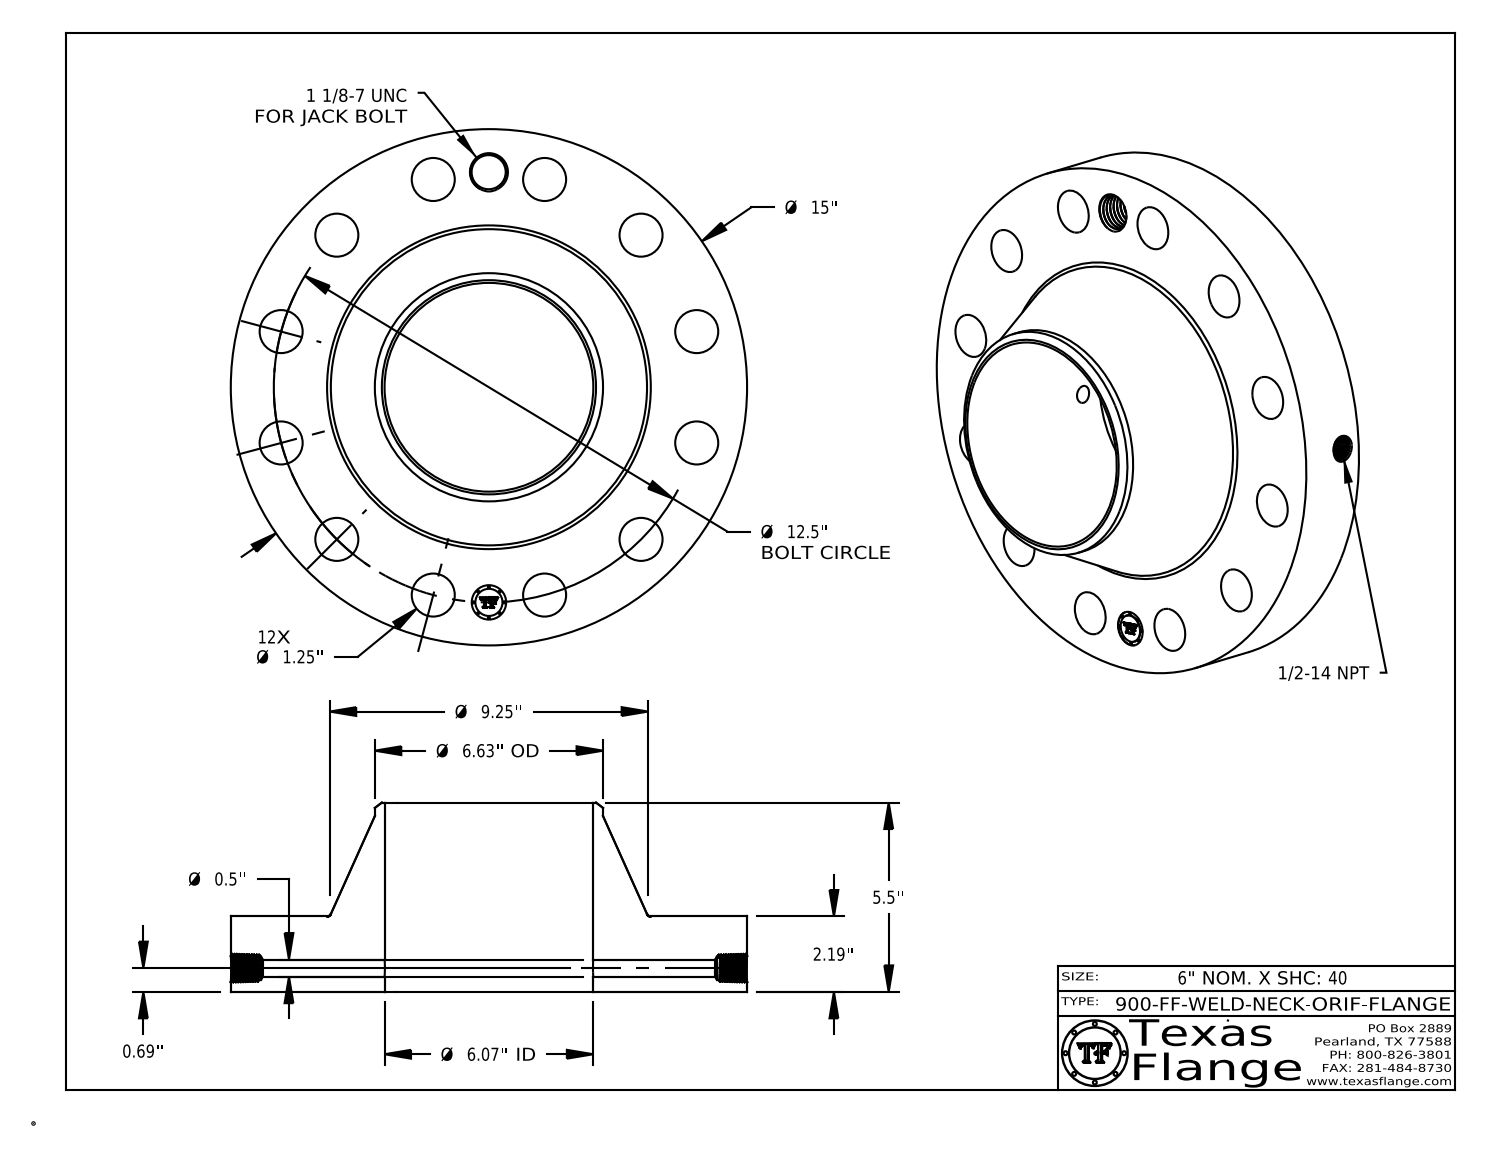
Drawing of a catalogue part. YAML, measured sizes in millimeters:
part_name: "900-FF-WELD-NECK"
step_written_by: "CATIA V5 STEP AP214 (AUTOMOTIVE_DESIGN)"
units: millimeters
bodies: {solids: 1, faces: 777, planar: 368, cylindrical: 100, other: 309}
overall_size: [381, 381, 139.7]
volume: 5749000
surface_area: 423200
round_holes:
  - {diameter: 31.8, count: 12}
  - {diameter: 12.7, count: 1}
  - {diameter: 17.1, count: 1}
  - {diameter: 25, count: 1}
  - {diameter: 25.4, count: 1}
  - {diameter: 154.1, count: 1}
round_bosses_or_shafts:
  - {diameter: 1.5, count: 8}
  - {diameter: 381, count: 1}
  - {diameter: 168.4, count: 1}
  - {diameter: 20, count: 1}
face_to_face_distances: [55.6, 139.7, 84.1, 55.2, 0.4, 84.5, 7.6, 7.4, 1.4, 6.3]
hole_center_spacings: [158.8, 306.7, 82.2, 224.5, 275, 317.5, 41.4, 82.2]
